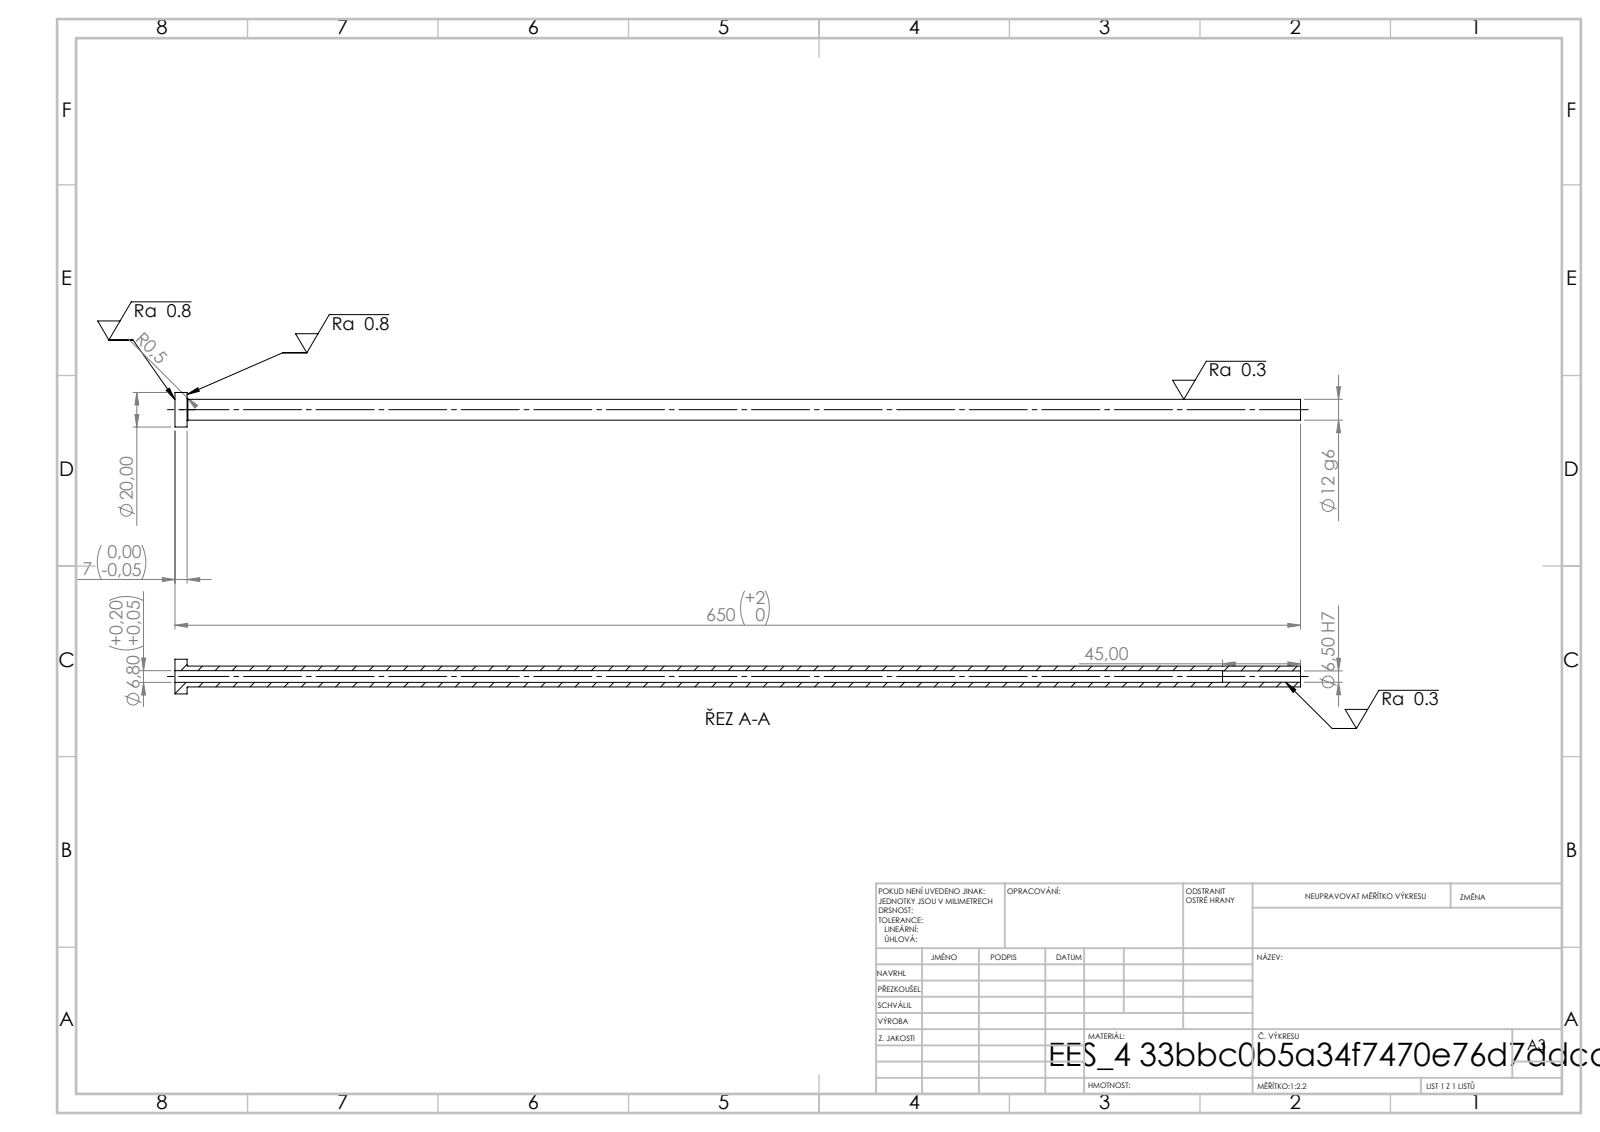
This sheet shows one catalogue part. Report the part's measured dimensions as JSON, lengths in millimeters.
{"step_written_by": "SolidWorks 2019 (CONFIG_CONTROL_DESIGN)", "units": "millimeters", "bodies": {"solids": 1, "faces": 14, "planar": 4, "cylindrical": 8, "other": 2}, "overall_size": [650, 20, 20], "volume_mm3": 51458, "surface_area_mm2": 39078, "round_holes": [[6.5, 1], [6.8, 1]], "round_bosses_or_shafts": [[20, 1], [12, 1]], "face_to_face_distances": [7, 650, 643, 605, 598, 45]}
